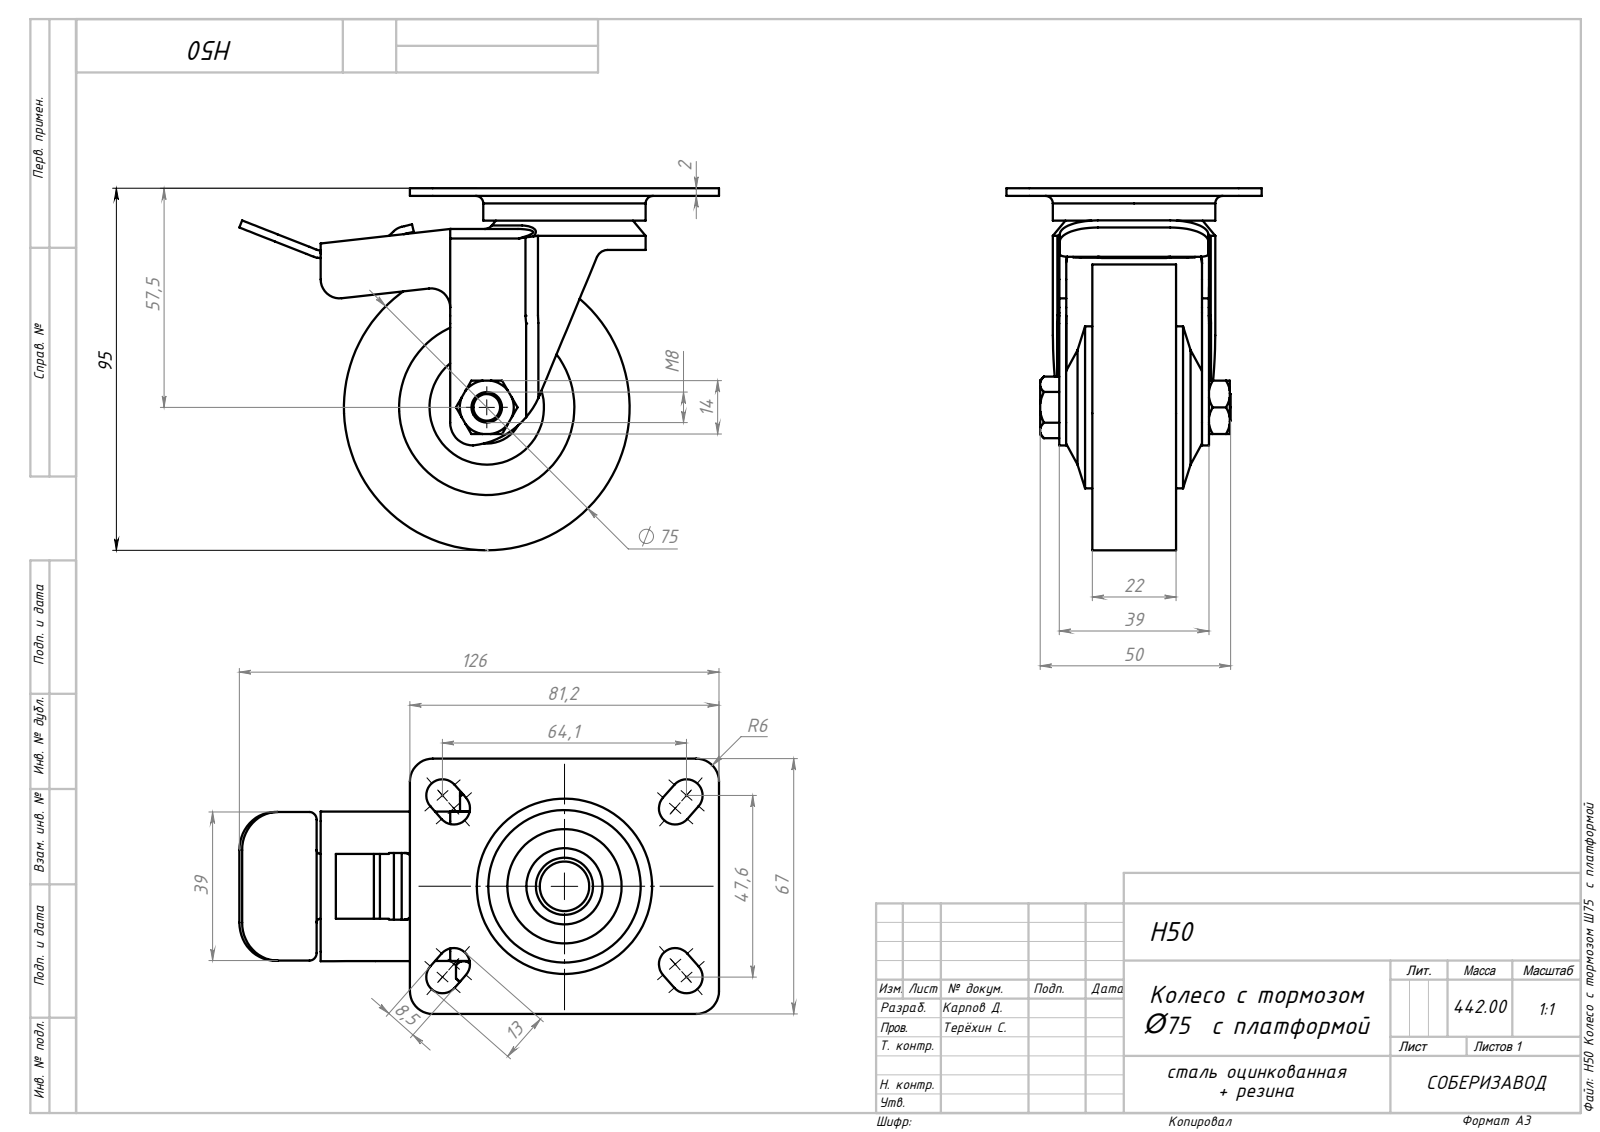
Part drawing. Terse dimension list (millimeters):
name: H50 Тормоз_00; H50 Гайка_00; H50 Защита_00; H50 Опора_00 (+6 more)
written by: SolidWorks 2024 (AUTOMOTIVE_DESIGN)
unit: mm
bodies: 9 solids, 304 faces (111 planar, 111 cylindrical, 82 other)
size: 125.92 × 95 × 67
volume: 113 942 mm³; area: 60 060 mm²
holes: 1× ⌀7, 1× ⌀8, 1× ⌀8.2, 1× ⌀12, 1× ⌀12.5, 1× ⌀20, 1× ⌀39.16, 1× ⌀40, 1× ⌀41.5
bosses: 1× ⌀75, 1× ⌀42.62, 1× ⌀42.5, 1× ⌀35, 1× ⌀30, 1× ⌀22, 1× ⌀15
rounds: 10× R2, 8× R4.25, 7× R2.5, 6× R10, 5× R6, 4× R1, 3× R4.5, 2× R5
face distances: 2, 22, 1.8, 9, 6.82, 28.82, 5, 4, 13, 15.82
